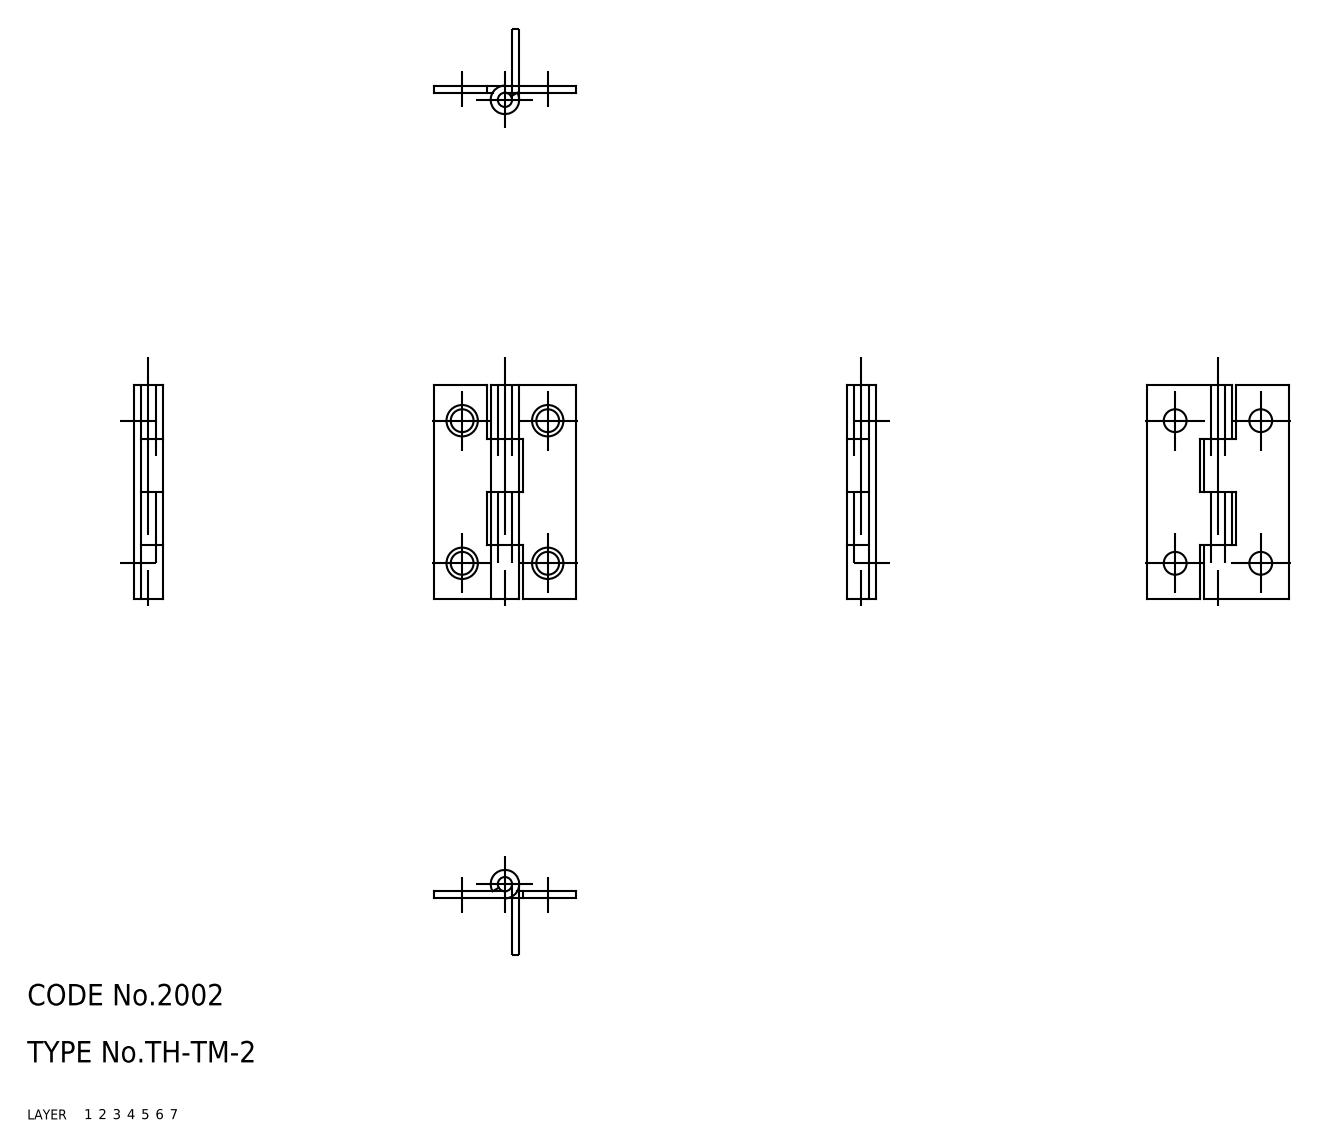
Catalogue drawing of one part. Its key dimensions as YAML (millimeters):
part_name: "shaft; hinge pieceB; hinge pieceA; TH_TM_2_21892_36"
step_written_by: "CADfix (AUTOMOTIVE_DESIGN)"
units: millimeters
bodies: {solids: 3, faces: 52, planar: 0, cylindrical: 0, other: 52}
overall_size: [30, 20, 4]
volume: 813
surface_area: 1910
